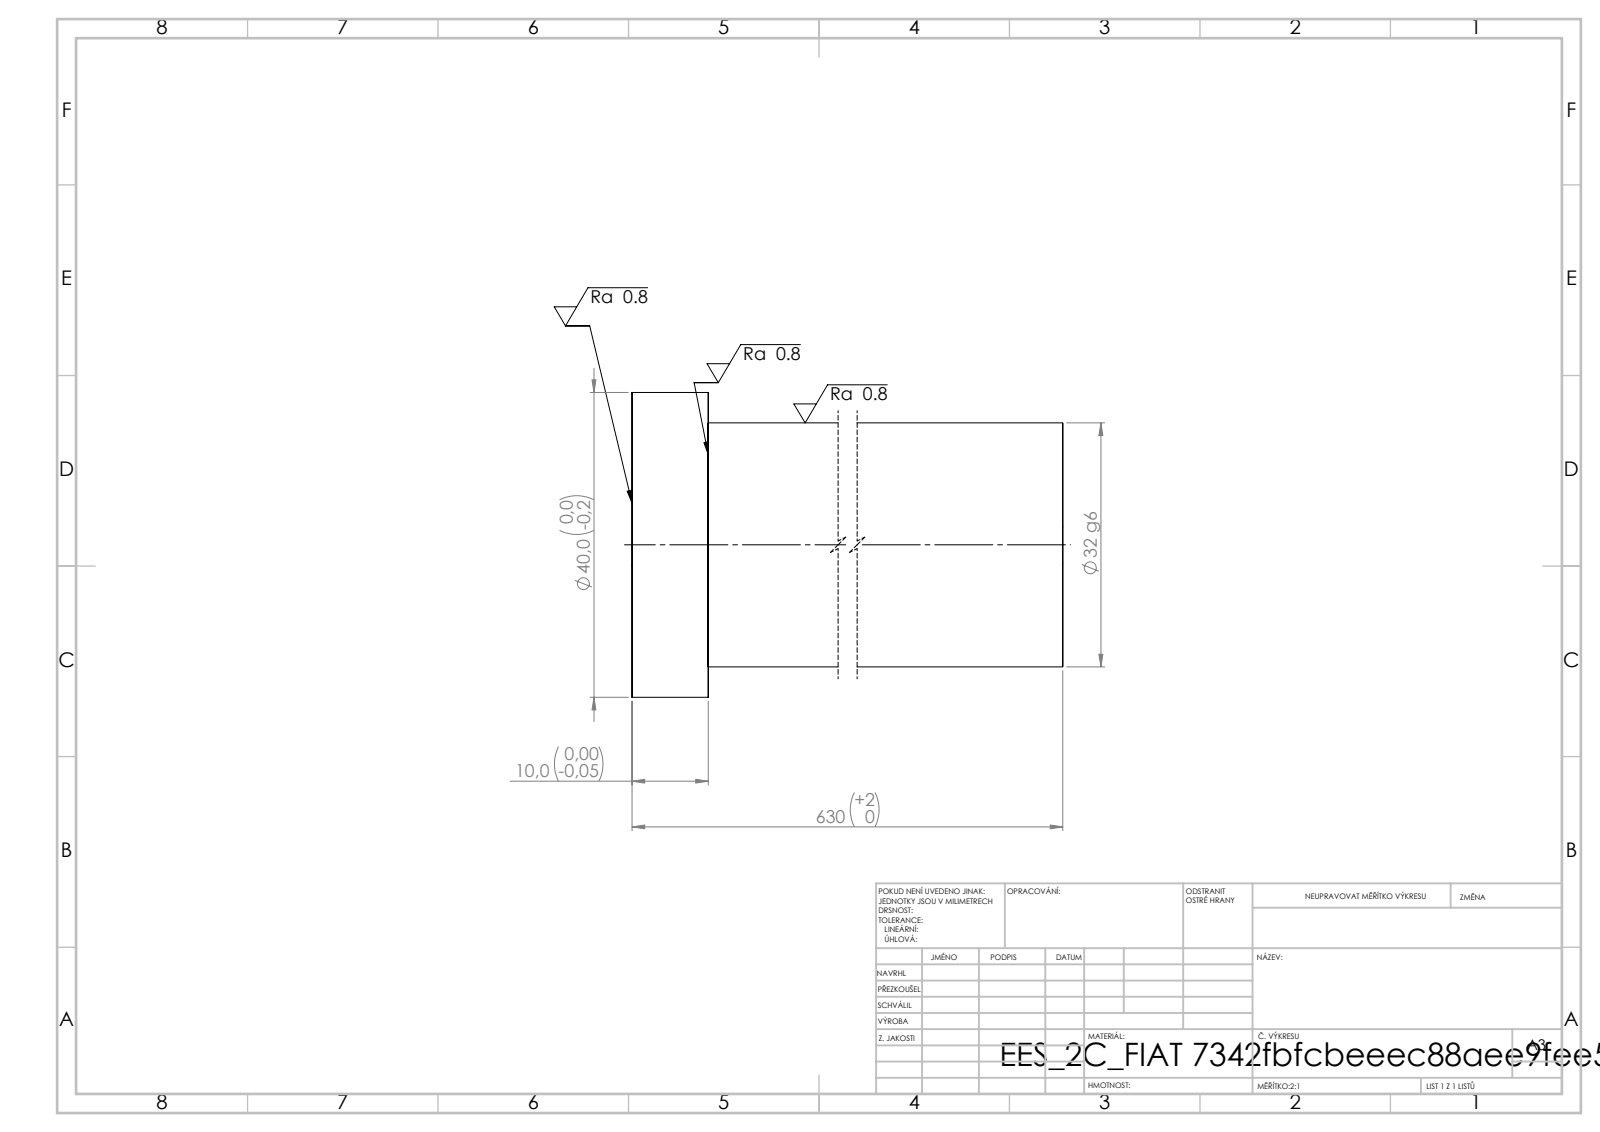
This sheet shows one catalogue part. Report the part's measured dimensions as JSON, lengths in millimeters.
{"step_written_by": "SolidWorks 2019 (CONFIG_CONTROL_DESIGN)", "units": "millimeters", "bodies": {"solids": 1, "faces": 7, "planar": 3, "cylindrical": 4, "other": 0}, "overall_size": [630, 40, 40], "volume_mm3": 511200, "surface_area_mm2": 66099, "round_bosses_or_shafts": [[40, 1], [32, 1]], "face_to_face_distances": [630, 10, 620]}
